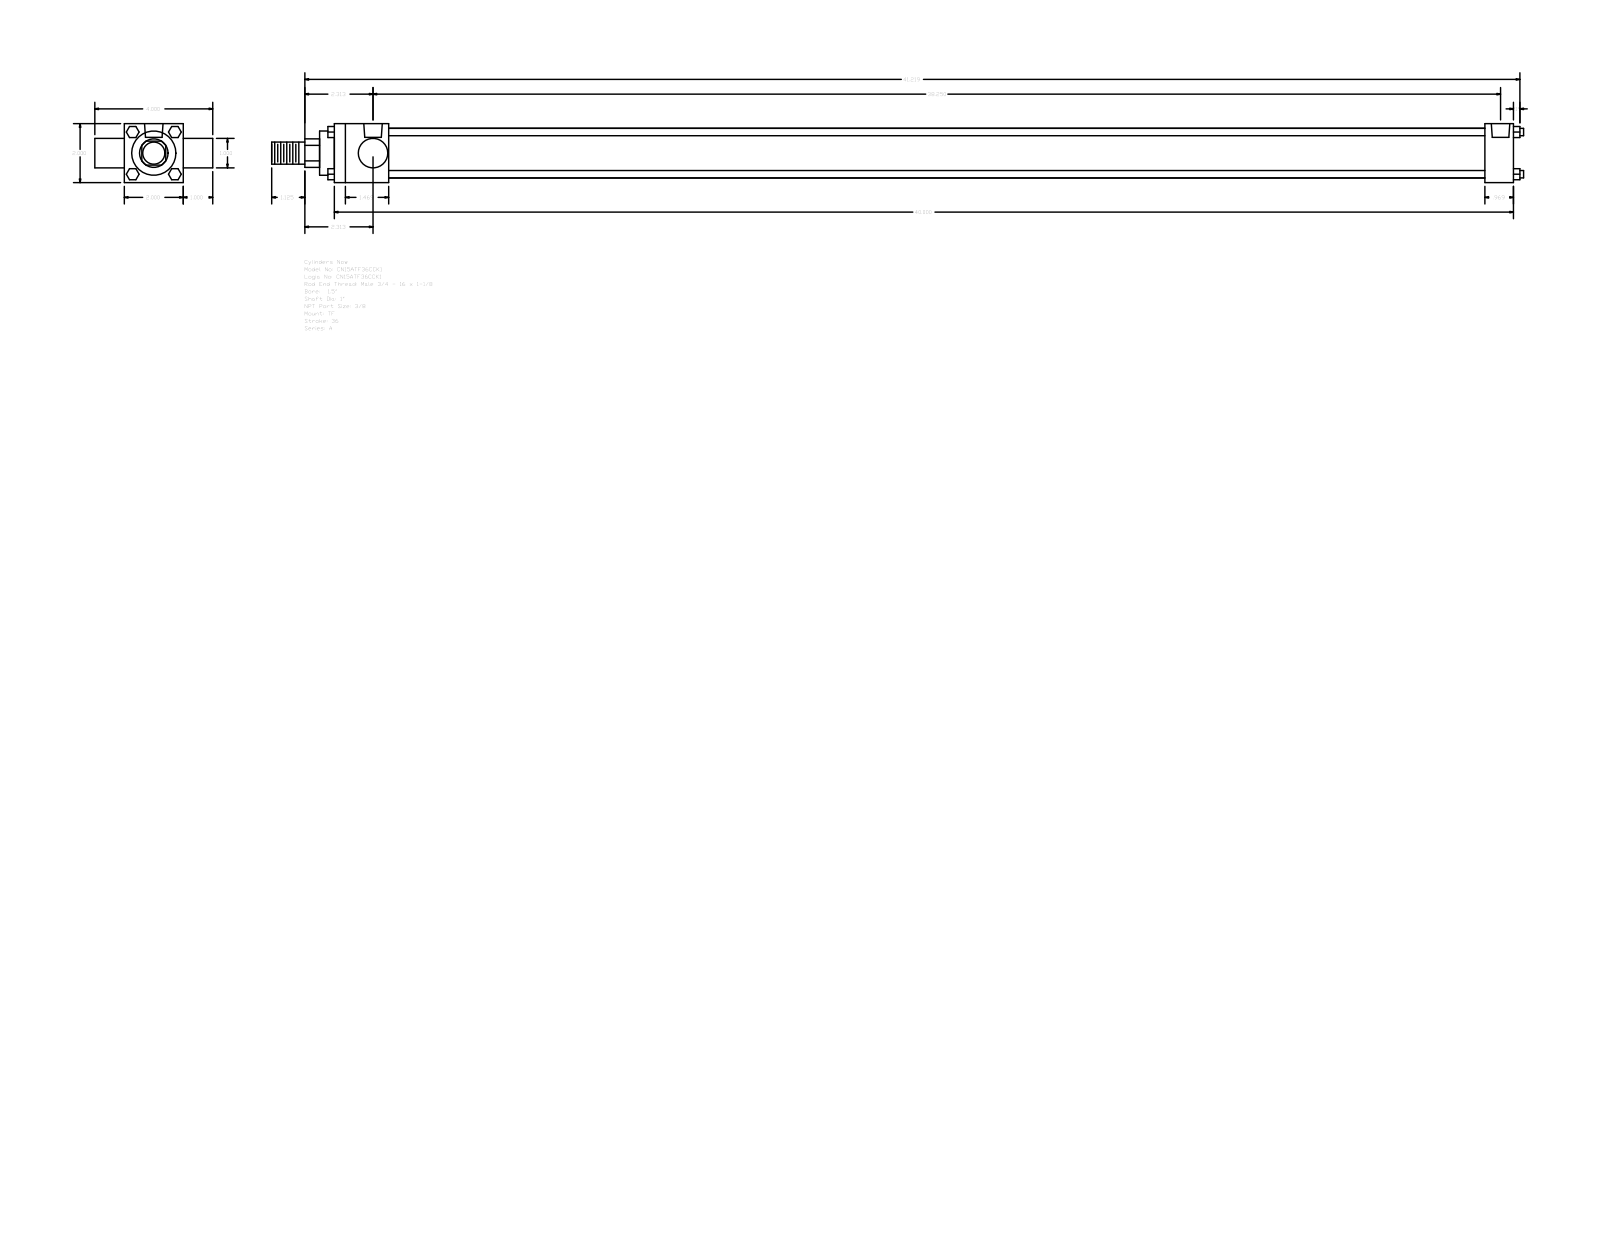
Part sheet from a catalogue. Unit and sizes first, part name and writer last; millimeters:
Units: millimetres
Overall size (bounding box): 1078.71 × 101.6 × 50.8
Round holes (diameter × count): ⌀5.56 ×3, ⌀15.93 ×2
Round bosses / shafts (diameter × count): ⌀6.35 ×4, ⌀25.4 ×2, ⌀42.93 ×1, ⌀38.1 ×1, ⌀19.05 ×1
Partial cylindrical surfaces — rounded edges, fillets, slot ends (radius × count): R12.29 ×1
Main face-to-face distances: 50.8, 25.4, 1016, 76.2, 46.83, 991.39, 944.56, 969.17, 24.61, 12.7
Hole centre spacings: 3.97, 967.58, 963.61, 971.55
Bodies: 0 solids, 120 faces (92 planar, 28 cylindrical, 0 other)
Part name (STEP PRODUCT): A_TF__0150_1
STEP written by: GSSL Pune (CONFIG_CONTROL_DESIGN)
